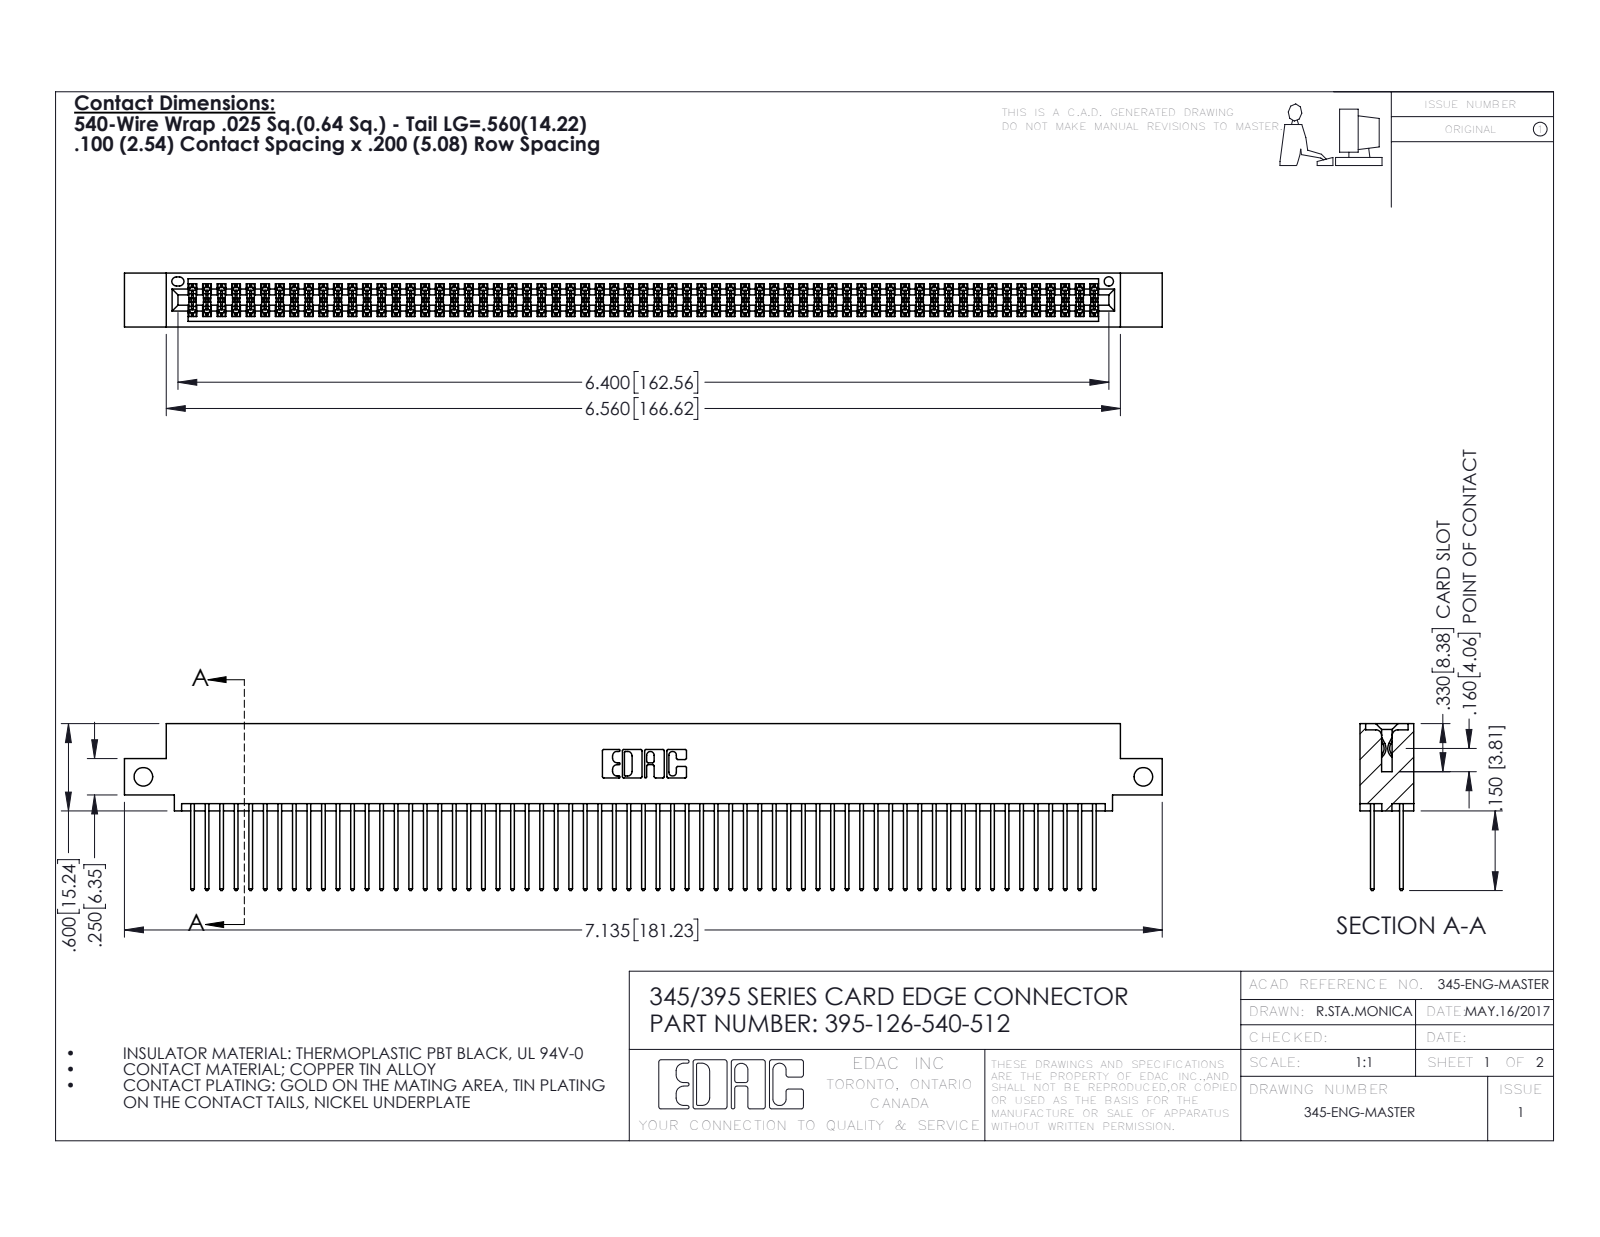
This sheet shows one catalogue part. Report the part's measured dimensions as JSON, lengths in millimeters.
{"part_name": "395-126-540-512; 345-292-001_345-293-140; 345 Part_0.110 Offset - Side Mount", "step_written_by": "SolidWorks 2016 (CONFIG_CONTROL_DESIGN)", "units": "millimeters", "bodies": {"solids": 127, "faces": 6430, "planar": 4242, "cylindrical": 2188, "other": 0}, "overall_size": [181.2, 29.1, 9.4], "volume_mm3": 18120, "surface_area_mm2": 29360, "round_holes": [[3.3, 2], [1.6, 1]], "partial_cylinders_radius": [[0.2, 189], [0.3, 126], [0.3, 22], [0.2, 6], [0.8, 6], [0.7, 3], [0.4, 2], [0.5, 2]], "face_to_face_distances": [1.8, 7.6, 5.1, 2.5, 6.9, 0.6, 5.7, 9.4, 4.4, 3.8], "hole_center_spacings": [174.6]}
